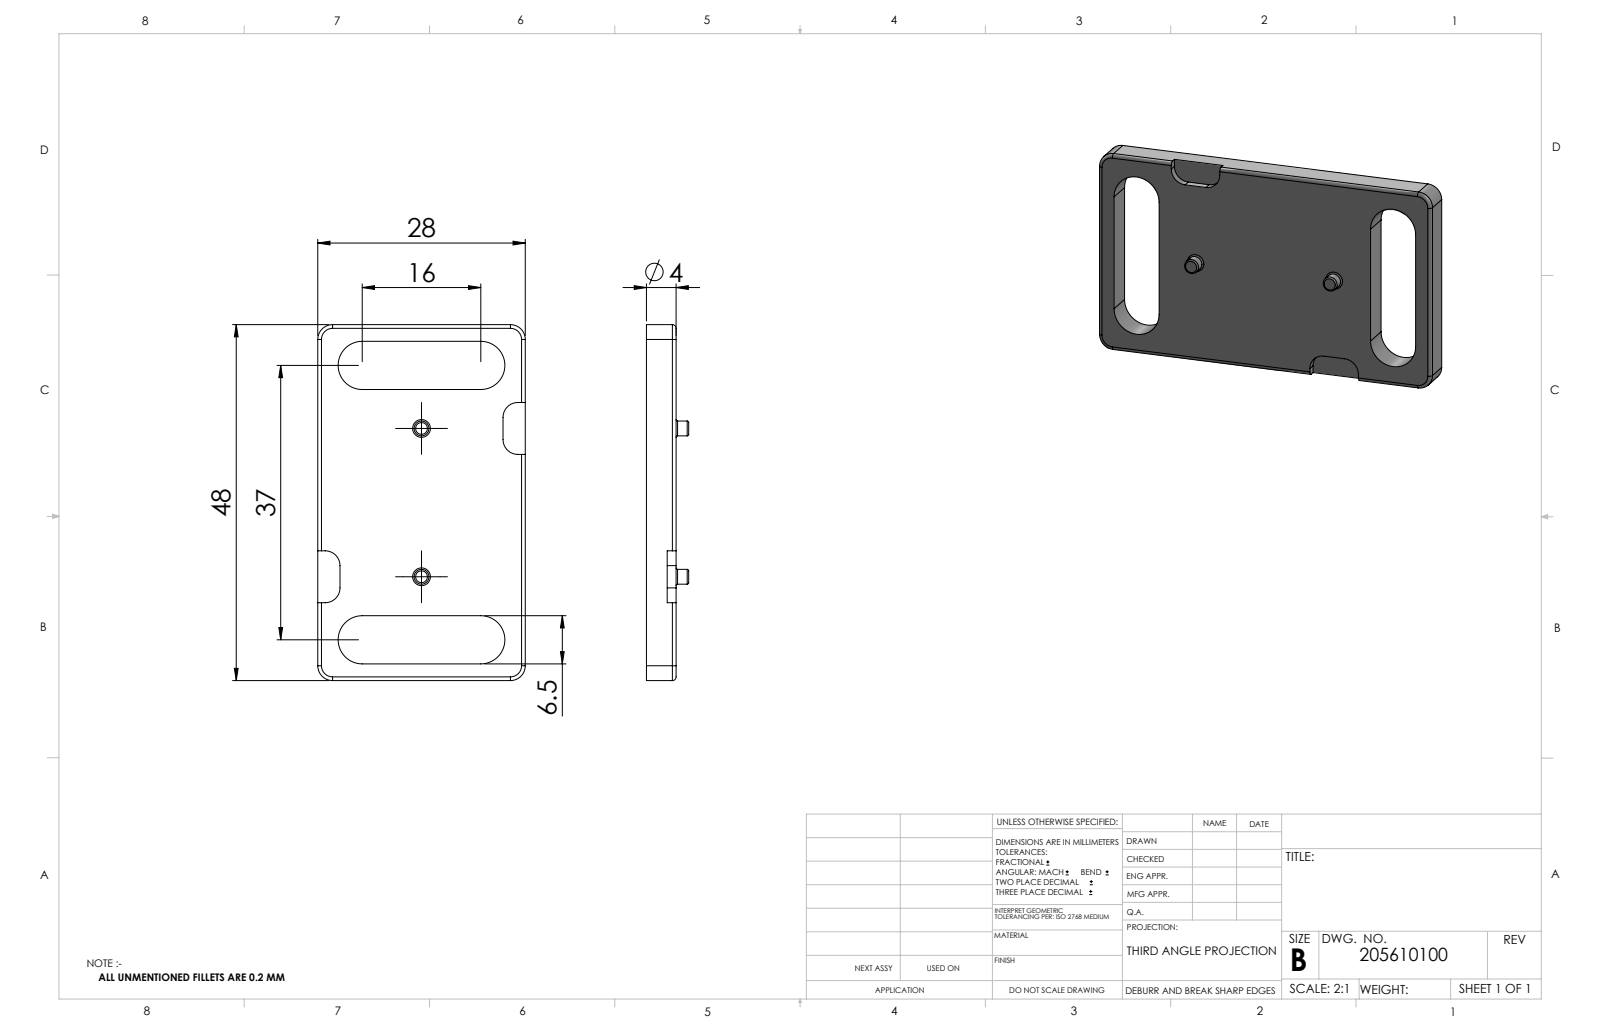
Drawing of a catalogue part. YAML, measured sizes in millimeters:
part_name: "205610100_c_1"
step_written_by: "SolidWorks 2014 (CONFIG_CONTROL_DESIGN)"
units: millimeters
bodies: {solids: 1, faces: 64, planar: 22, cylindrical: 26, other: 16}
overall_size: [48, 28, 5.7]
volume: 4206
surface_area: 3175
round_holes:
  - {diameter: 1.95, count: 2}
round_bosses_or_shafts:
  - {diameter: 2, count: 2}
partial_cylinders:
  - {radius: 2, count: 8}
  - {radius: 0.5, count: 4}
  - {radius: 3.25, count: 4}
face_to_face_distances: [4, 28, 8.75, 39.25, 2.25, 45.75, 6.5, 37, 48, 30.5]
hole_center_spacings: [20]
